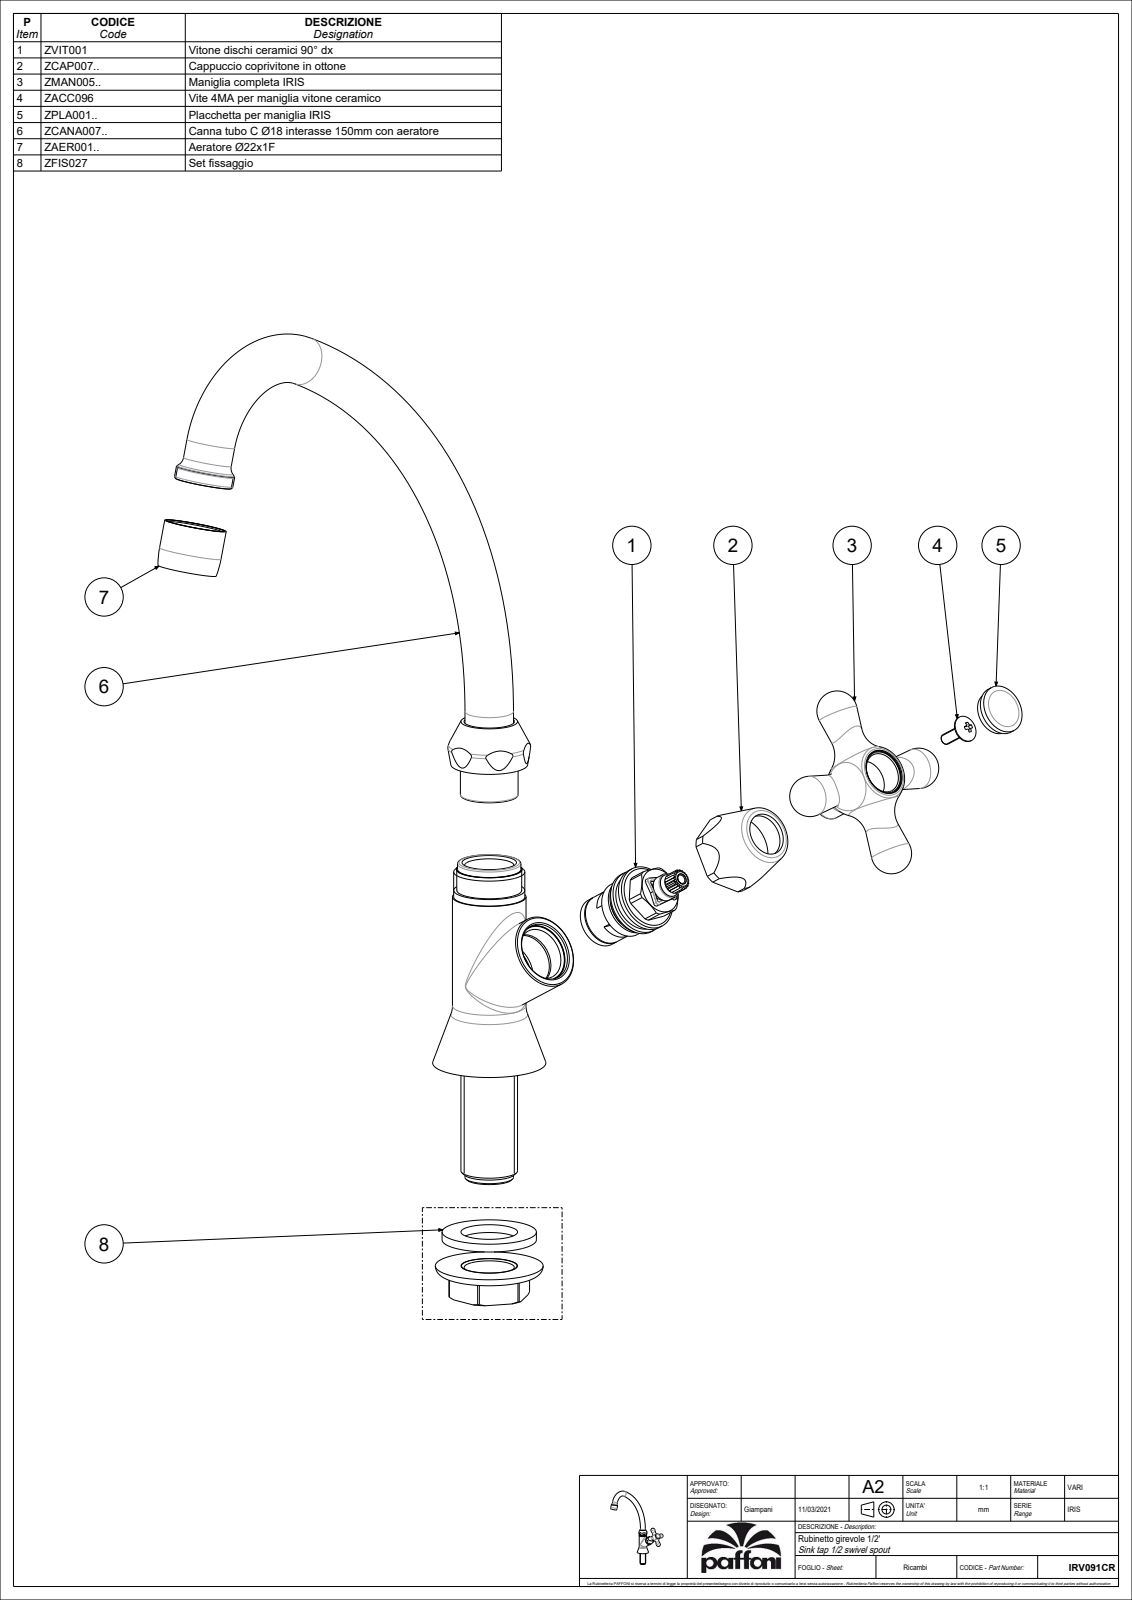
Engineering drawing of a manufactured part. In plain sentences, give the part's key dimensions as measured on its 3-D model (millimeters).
The part is named "IRV091CR". Its 3-D file was written by "CREO PARAMETRIC BY PTC INC, 2020044 (CONFIG_CONTROL_DESIGN)". It is 1 solid with 123 faces: 21 planar, 24 cylindrical and 78 other. Overall it measures 255.5 by 199.99 by 109.61 millimeters. Its volume is 182 802 cubic millimeters and its surface area 36 133 square millimeters. Round bosses or shafts: 3 of diameter 18, 1 of diameter 27.3, 1 of diameter 27.2, 1 of diameter 26.4, 1 of diameter 23.2, 1 of diameter 22, 1 of diameter 13.5. Partial cylindrical surfaces (rounded edges, fillets, slot ends): 1 of radius 14.5. The main face-to-face distances are 26.5, 29, 1.25, 27.75, 86.2, 69.7, 16.5, 24, 17, 63.8.
